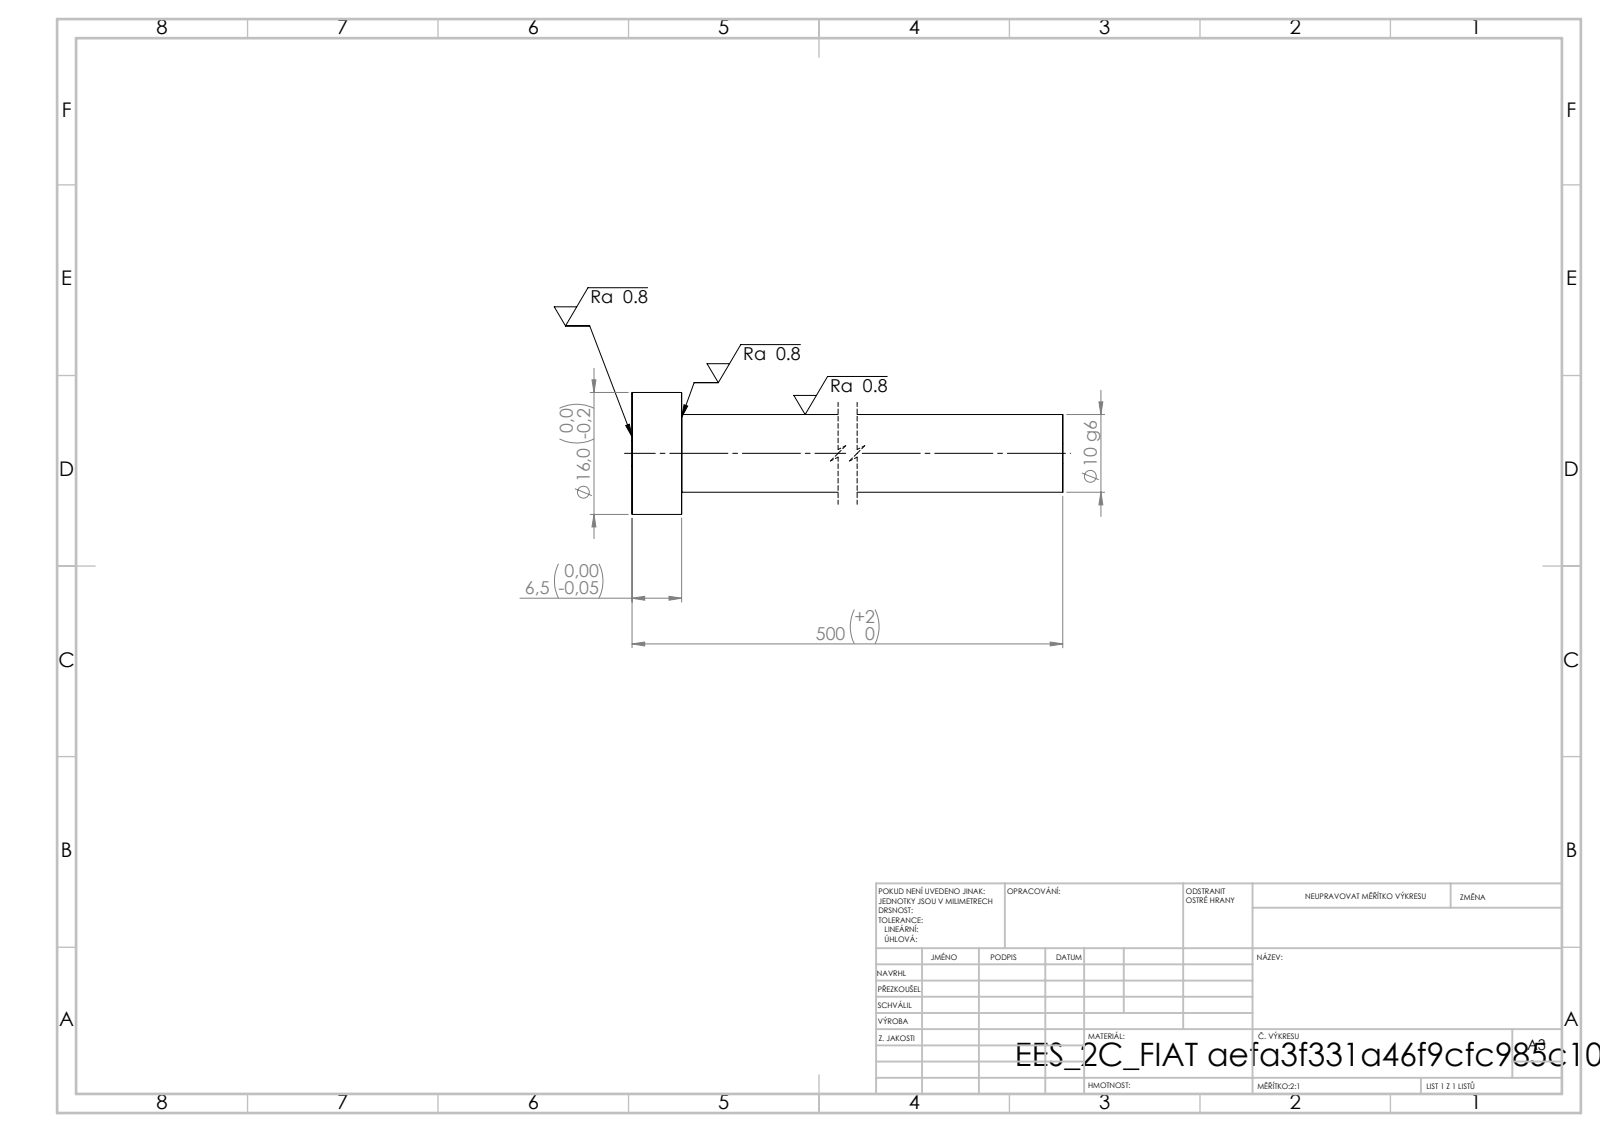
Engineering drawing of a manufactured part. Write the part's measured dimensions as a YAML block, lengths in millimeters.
step_written_by: "SolidWorks 2019 (CONFIG_CONTROL_DESIGN)"
units: millimeters
bodies: {solids: 1, faces: 7, planar: 3, cylindrical: 4, other: 0}
overall_size: [500, 16, 16]
volume: 41632
surface_area: 16543
round_bosses_or_shafts:
  - {diameter: 16, count: 1}
  - {diameter: 10.2, count: 1}
face_to_face_distances: [6.5, 500, 493.5]
